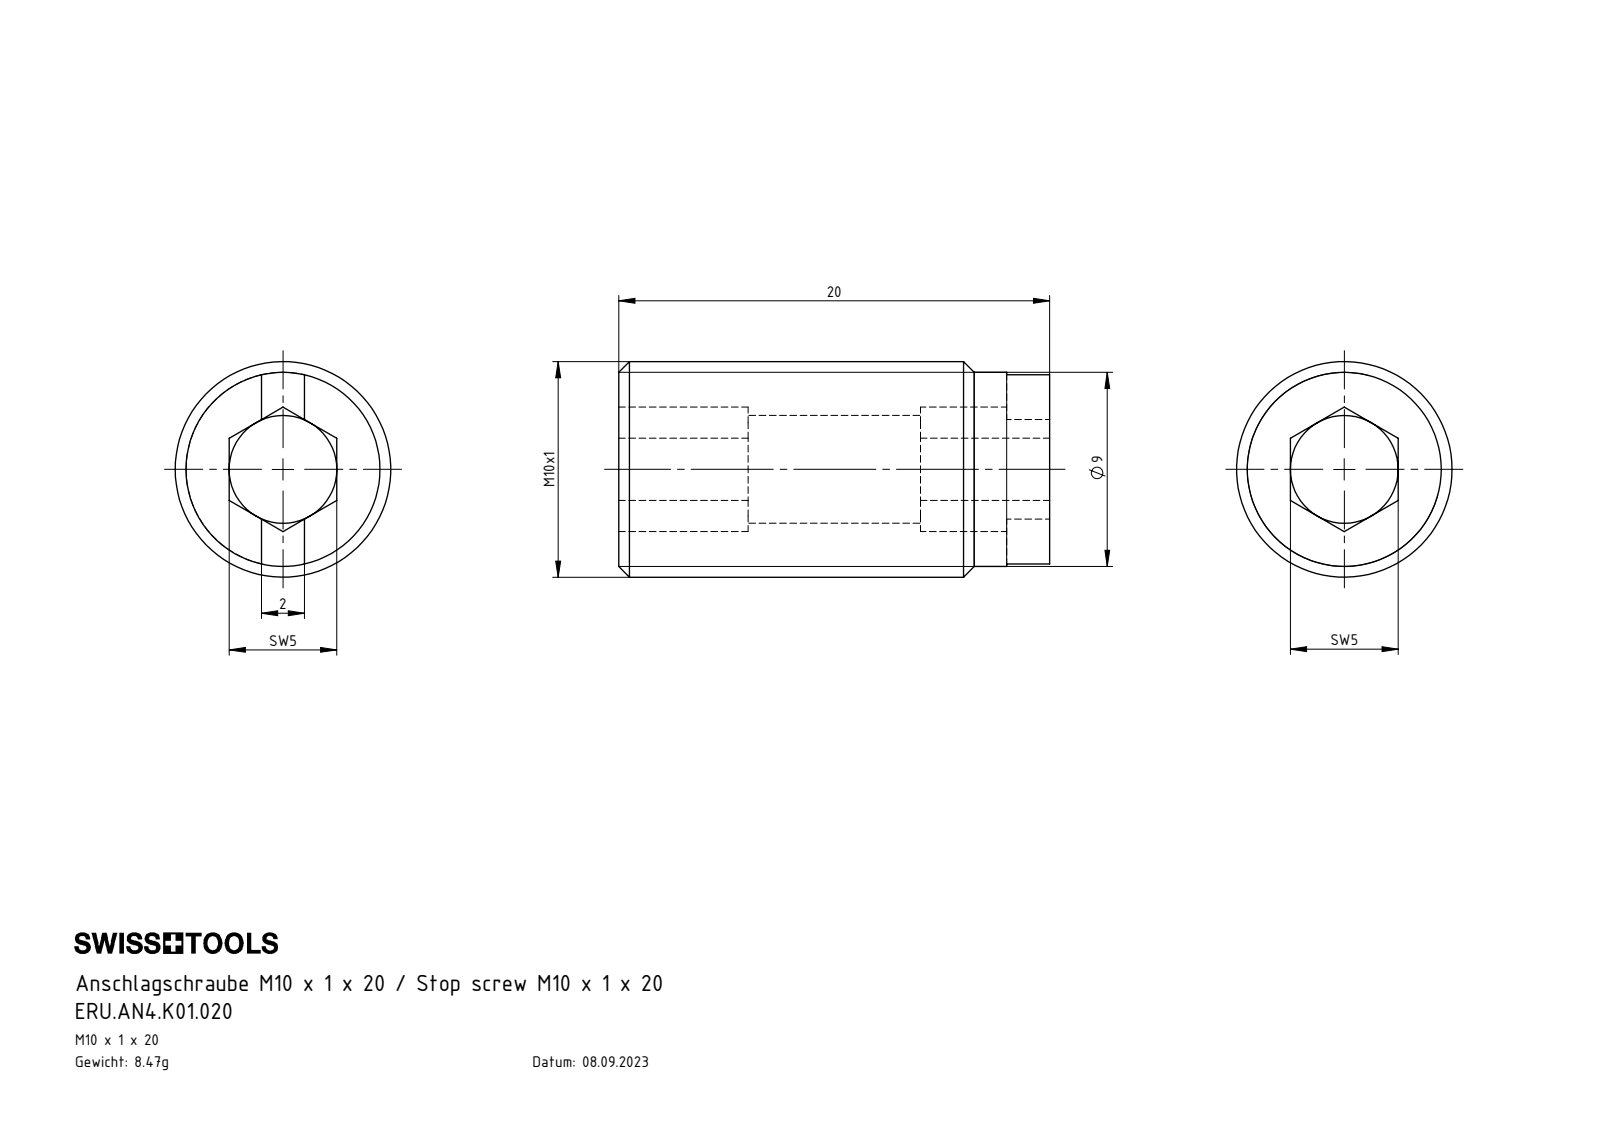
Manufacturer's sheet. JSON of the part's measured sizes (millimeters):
{"part_name": "ERU.AN4.K01.020", "step_written_by": "SolidWorks 2017 (AUTOMOTIVE_DESIGN)", "units": "millimeters", "bodies": {"solids": 1, "faces": 43, "planar": 33, "cylindrical": 6, "other": 4}, "overall_size": [20, 10, 10], "volume_mm3": 1079, "surface_area_mm2": 1049, "round_holes": [[5, 1]], "round_bosses_or_shafts": [[10, 1], [9, 1]], "face_to_face_distances": [5, 20, 1.5, 3.5, 2, 18, 6, 14, 4, 8]}
